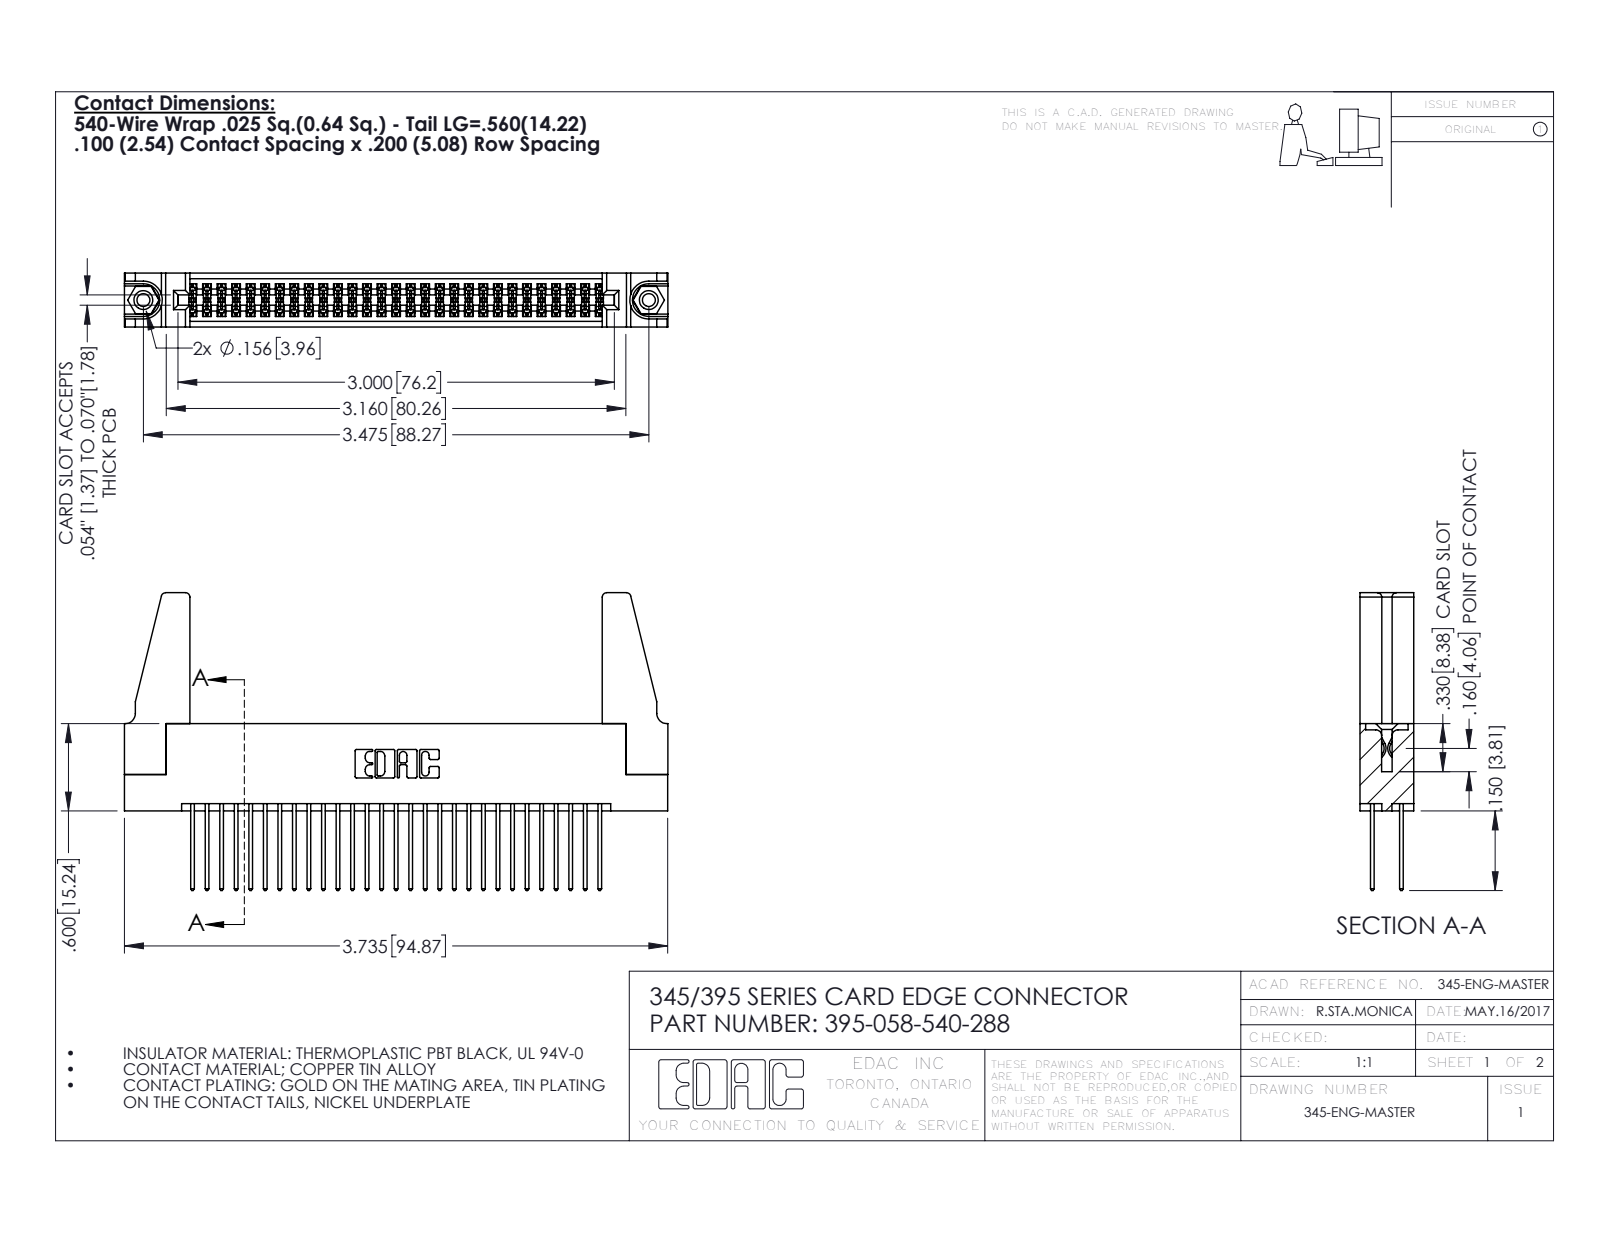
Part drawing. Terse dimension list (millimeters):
name: 345-220-078_345-220-088; 395-058-540-288; 345-292-001_345-293-140; 345 Part_Flush Mounting Lugs - 0.156 Dia-TH (+1 more)
written by: SolidWorks 2016 (CONFIG_CONTROL_DESIGN)
unit: mm
bodies: 63 solids, 3150 faces (2066 planar, 1068 cylindrical, 16 other)
size: 94.9 × 52 × 9.4
volume: 12 600 mm³; area: 17 660 mm²
holes: 2× ⌀2.3, 2× ⌀3.2, 2× ⌀4, 1× ⌀1.6
bosses: 2× ⌀3.9
rounds: 87× R0.2, 58× R0.3, 22× R0.3, 8× R0.8, 6× R0.2, 6× R0.8, 3× R0.7, 2× R0.4
face distances: 1.8, 7.6, 5.1, 9.4, 2.5, 6.9, 0.6, 5.7, 4.4, 3.8
hole spacings: 6.9, 82.3, 88.3
